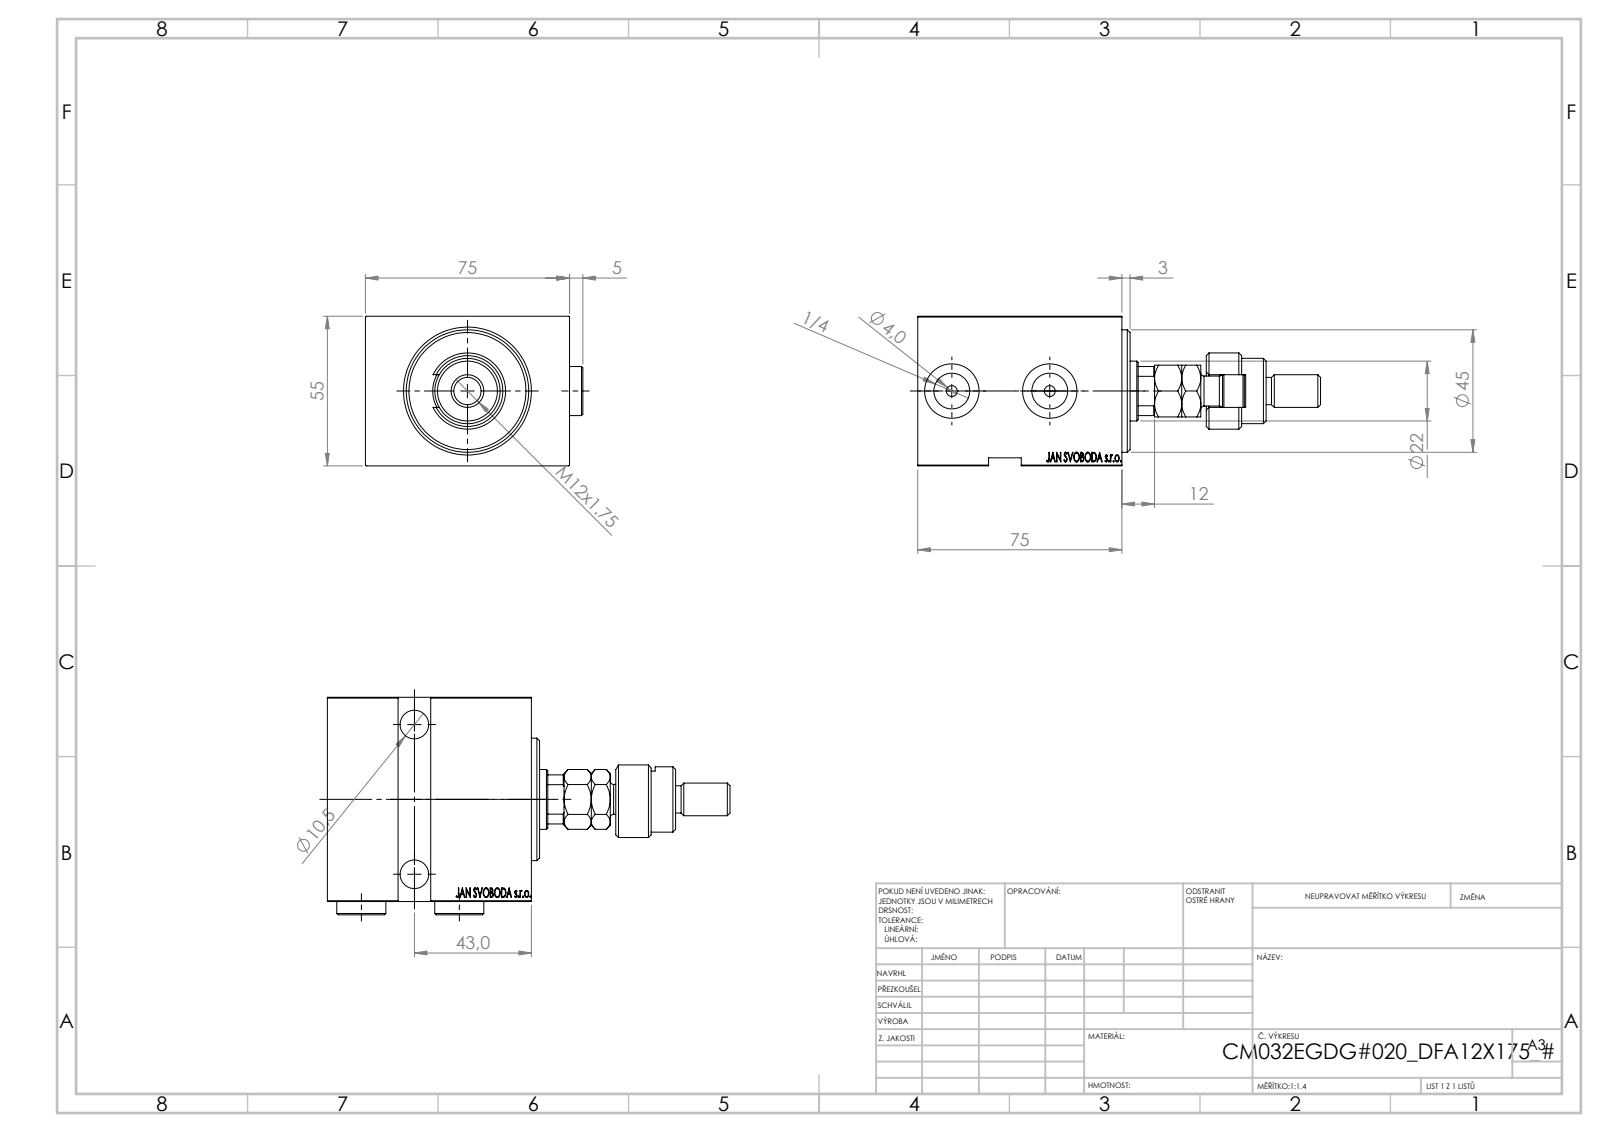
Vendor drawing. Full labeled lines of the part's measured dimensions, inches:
Part name (STEP PRODUCT): Zatka_OIL_PORT; V450CM_E_VCP; V450CM_E_Body; MFA (+2 more)
STEP written by: SolidWorks 2019 (CONFIG_CONTROL_DESIGN)
Units: inches
Bodies: 7 solids, 984 faces (471 planar, 71 cylindrical, 442 other)
Overall size (bounding box): 5.827 × 3.146 × 2.165
Volume: 18.47 in³ · Surface area: 97.82 in²
Round holes (diameter × count): ⌀0.413 ×3, ⌀0.157 ×2, ⌀0.518 ×2, ⌀0.65 ×2, ⌀0.787 ×2, ⌀0.866 ×1, ⌀1.004 ×1, ⌀1.26 ×1, ⌀1.772 ×1
Round bosses / shafts (diameter × count): ⌀0.709 ×3, ⌀1.339 ×1, ⌀1.102 ×1, ⌀0.945 ×1, ⌀0.472 ×1, ⌀0.433 ×1, ⌀0.394 ×1
Partial cylindrical surfaces — rounded edges, fillets, slot ends (radius × count): R0.384 ×1, R0.413 ×1
Main face-to-face distances: 2.953, 2.165, 0.197, 0.118, 2.559, 0.394, 2.756, 0.315, 2.362, 0.472
Hole centre spacings: 1.417, 2.165
